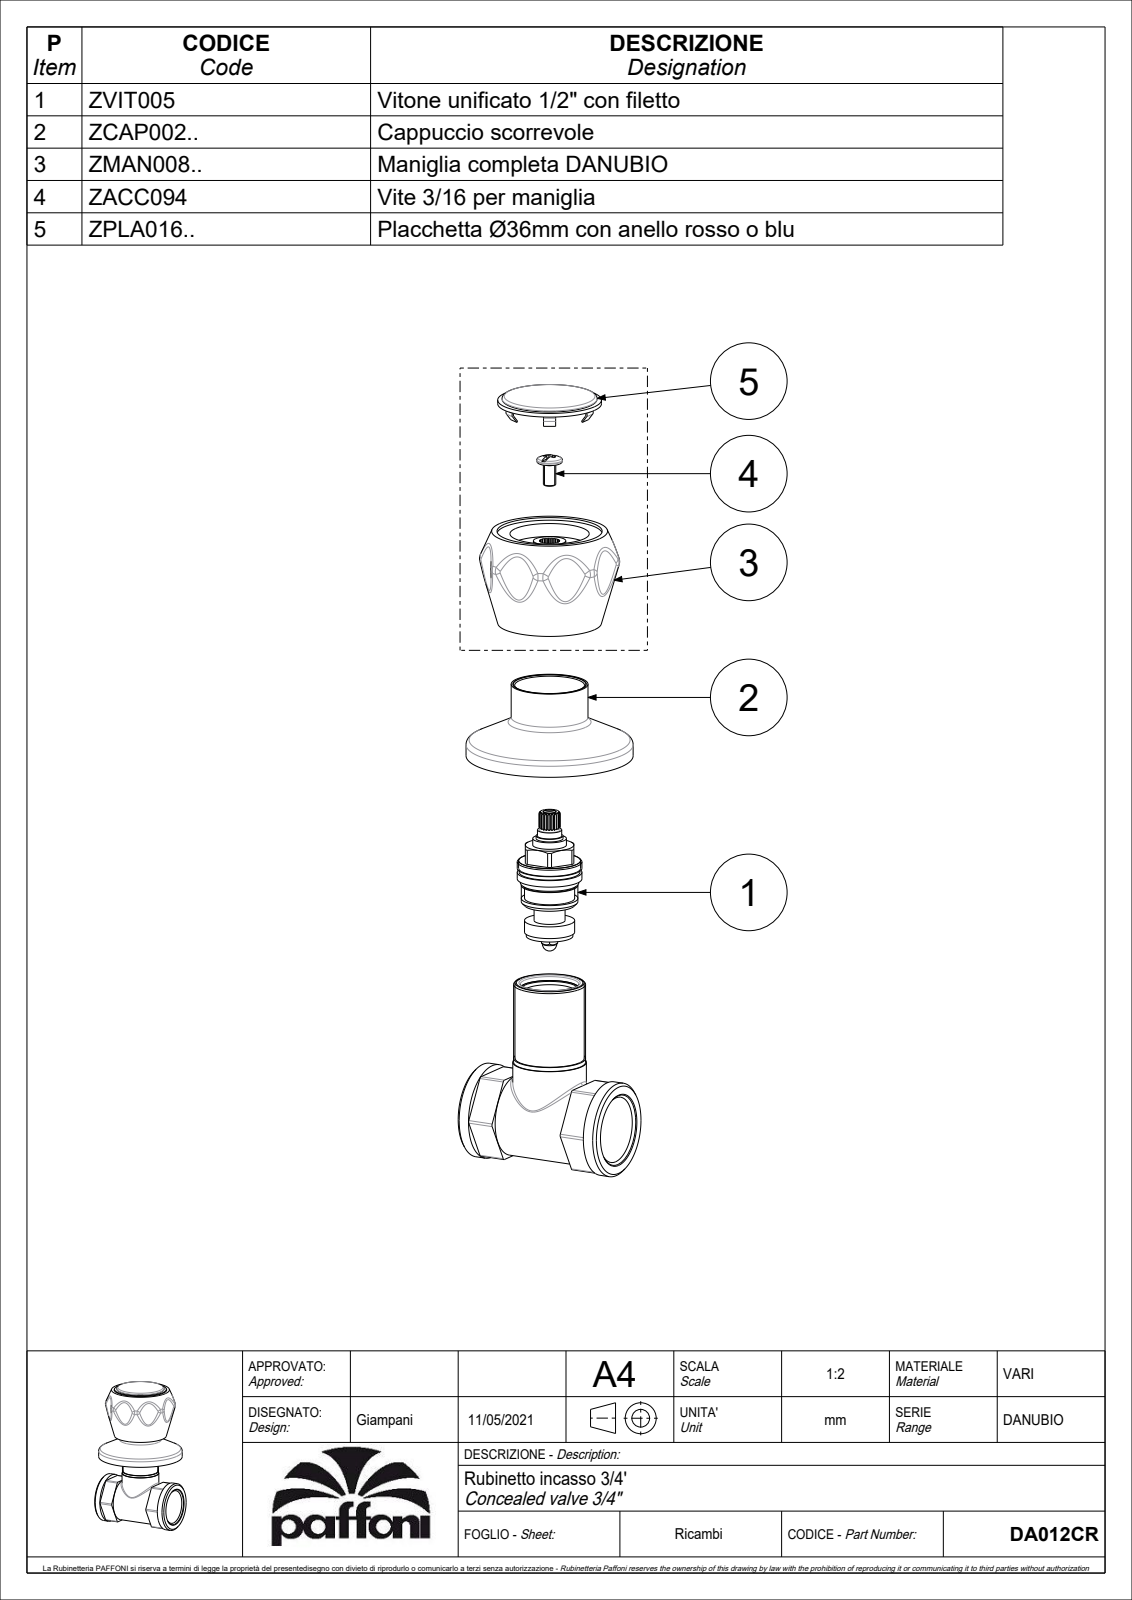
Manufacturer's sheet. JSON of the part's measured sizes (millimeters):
{"part_name": "DA010CR", "step_written_by": "CREO PARAMETRIC BY PTC INC, 2020044 (CONFIG_CONTROL_DESIGN)", "units": "millimeters", "bodies": {"solids": 2, "faces": 219, "planar": 81, "cylindrical": 60, "other": 78}, "overall_size": [62, 62, 58.5], "volume_mm3": 31276, "surface_area_mm2": 23896, "round_holes": [[25.9, 1], [35.8, 1], [39, 1], [59.4, 1]], "round_bosses_or_shafts": [[62, 1], [38.5, 1], [30.5, 1], [28.5, 1], [13, 1], [4.6, 1]], "partial_cylinders_radius": [[1, 12], [21.31, 8], [3.55, 1]], "face_to_face_distances": [6.7, 9.5, 2.8, 45.6, 52.3, 55.1, 55.5, 9.9, 3.2, 0.4]}
